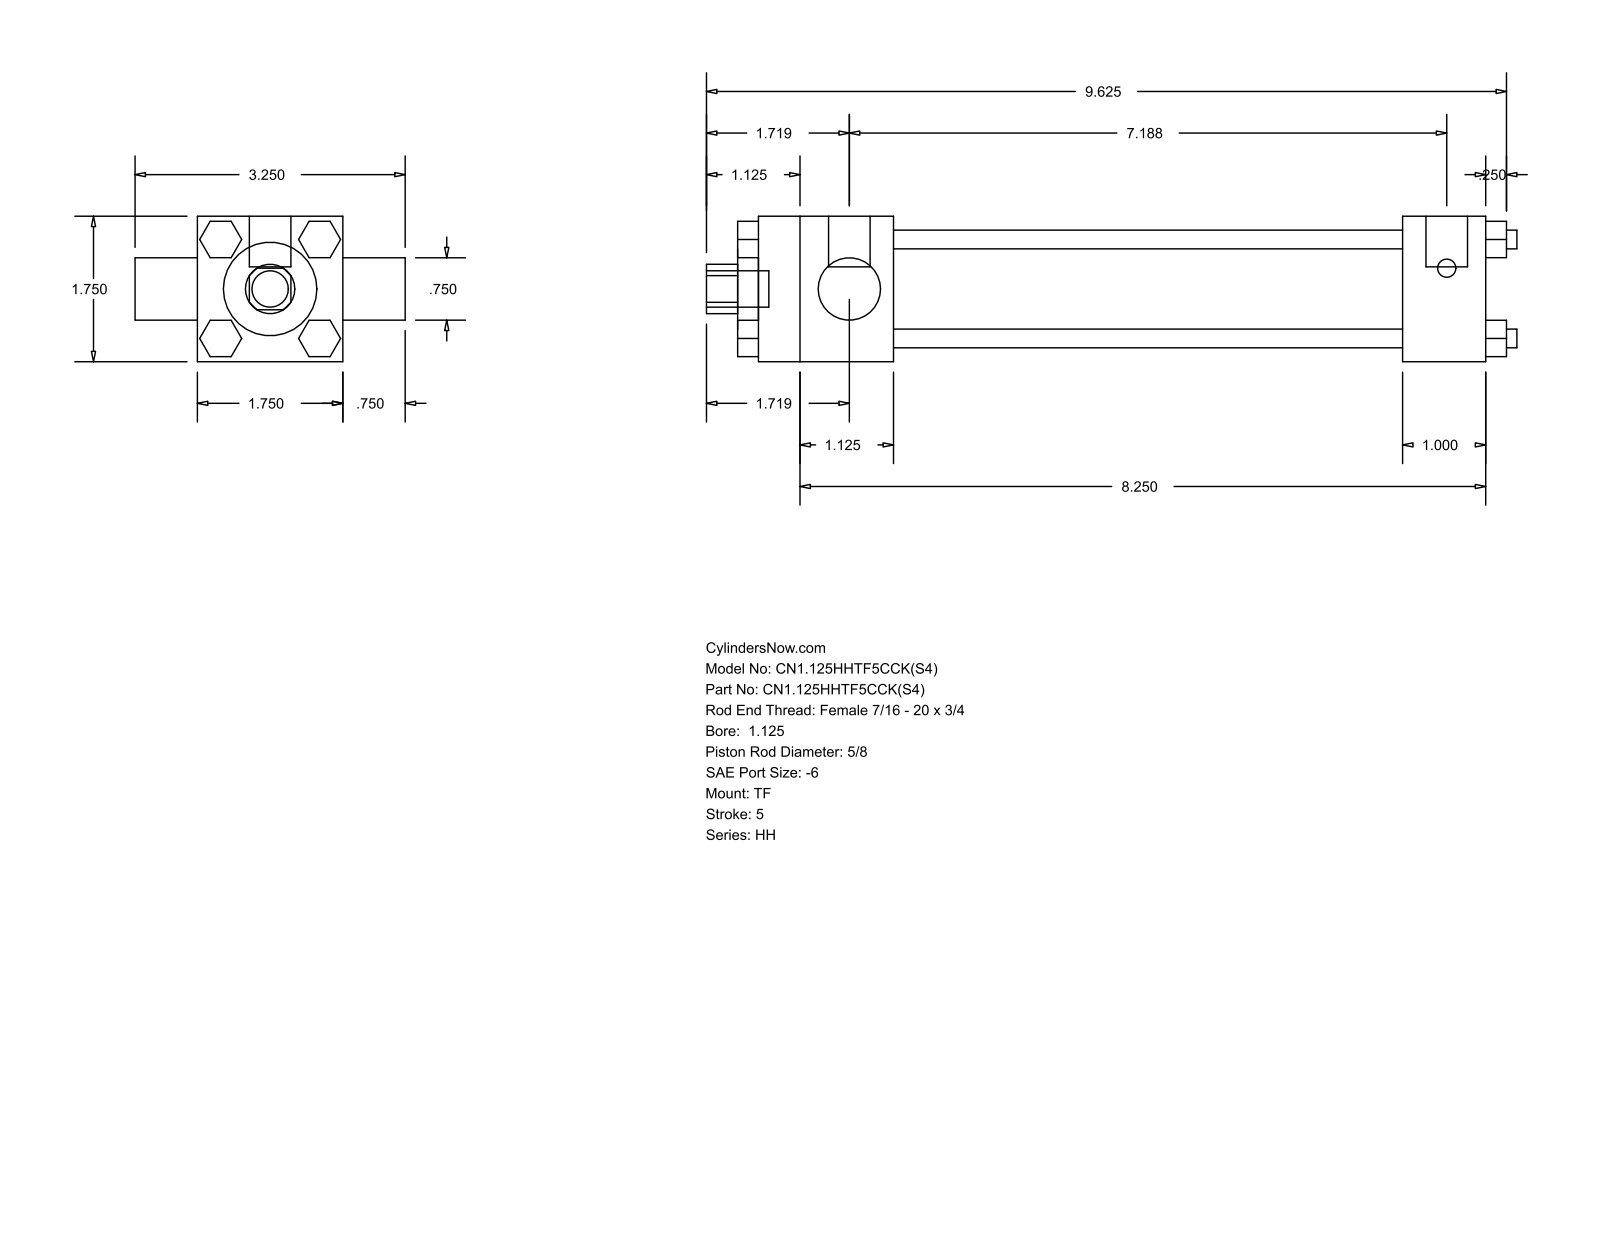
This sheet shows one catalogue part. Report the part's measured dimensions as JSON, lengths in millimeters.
{"part_name": "HH_TF__0112_0.625", "step_written_by": "GSSL Pune (CONFIG_CONTROL_DESIGN)", "units": "millimeters", "bodies": {"solids": 0, "faces": 120, "planar": 92, "cylindrical": 28, "other": 0}, "overall_size": [247.65, 82.55, 44.45], "round_holes": [[15.88, 1], [19.05, 1], [28.57, 1], [34.92, 1]], "round_bosses_or_shafts": [[5.71, 4], [5.56, 3], [12.7, 2], [11.11, 1]], "partial_cylinders_radius": [[7.54, 1]], "face_to_face_distances": [44.46, 6.35, 228.59, 11.11, 155.57, 180.97, 25.4, 41.27, 196.84, 222.24]}
